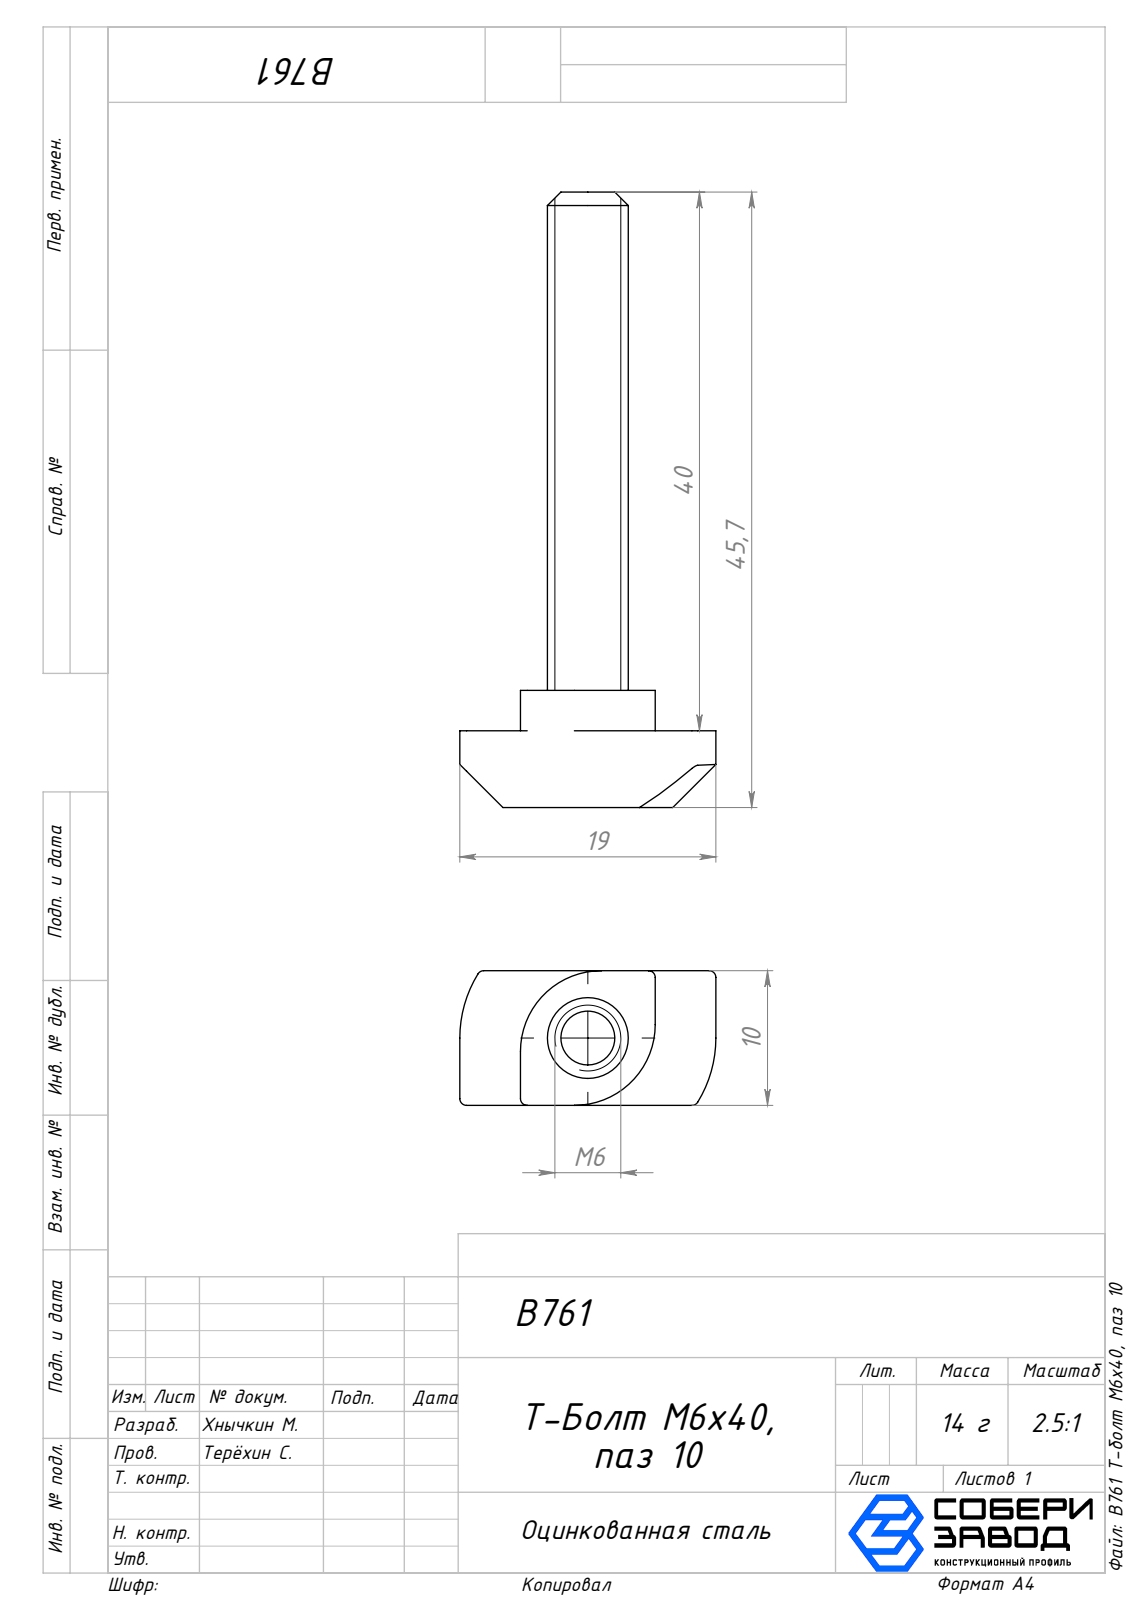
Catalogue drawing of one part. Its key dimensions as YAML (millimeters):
part_name: "B761 Т-болт М6х40, паз 10"
step_written_by: "SolidWorks 2025 (AUTOMOTIVE_DESIGN)"
units: millimeters
bodies: {solids: 1, faces: 29, planar: 13, cylindrical: 12, other: 4}
overall_size: [45.7, 19, 10]
volume: 2241
surface_area: 1413
round_bosses_or_shafts:
  - {diameter: 6, count: 1}
partial_cylinders:
  - {radius: 0.5, count: 6}
  - {radius: 6, count: 2}
  - {radius: 9.08, count: 2}
face_to_face_distances: [10, 5.7, 8.7, 3, 4.5, 14.5, 45.7, 40, 37, 19]
